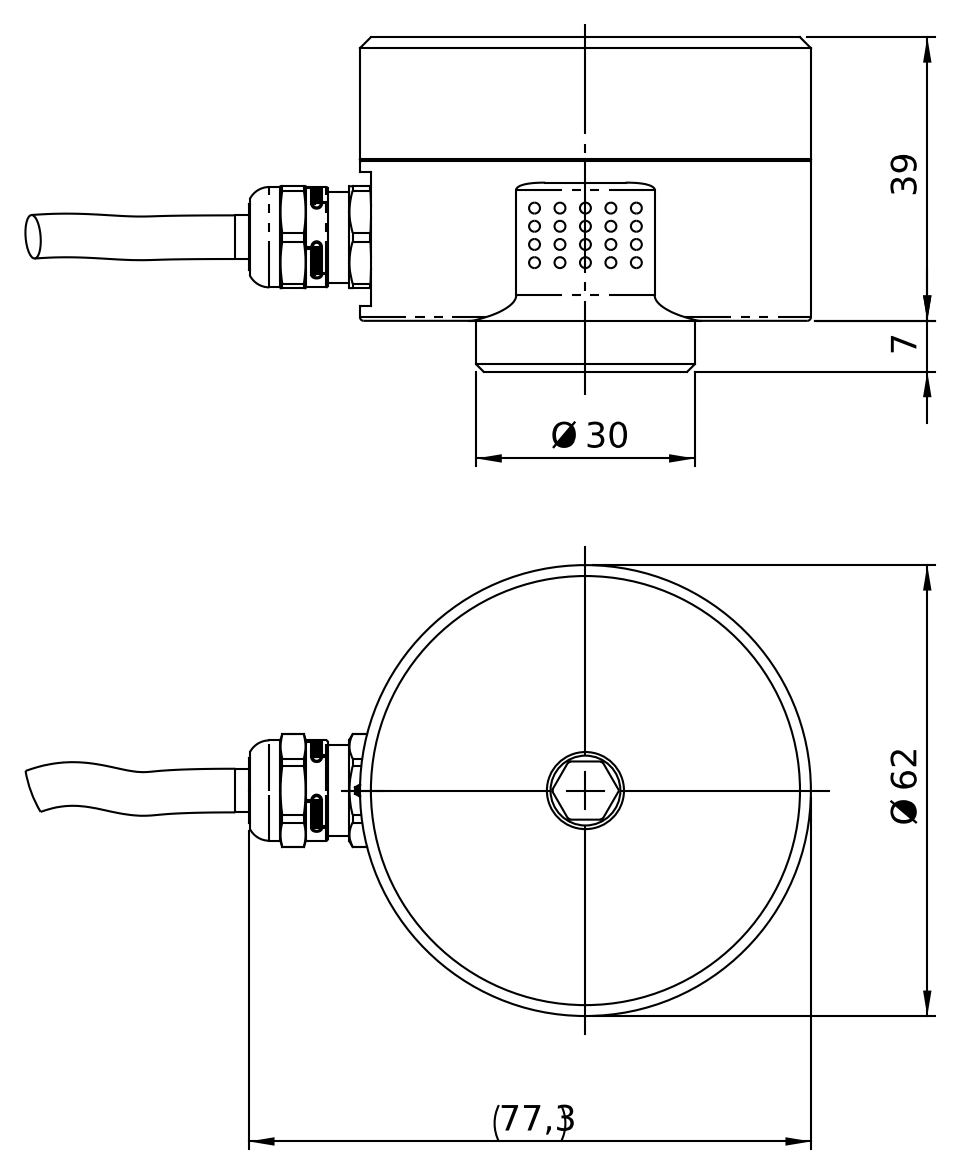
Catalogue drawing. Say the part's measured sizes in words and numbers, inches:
The part is named "02.117.022". Its 3-D file was written by "SolidWorks 2020 (AUTOMOTIVE_DESIGN)". It is 1 solid with 524 faces: 368 planar, 84 cylindrical and 72 other. Overall it measures 4.252 by 2.441 by 1.811 inches. Its volume is 7.271 cubic inches and its surface area 27.91 square inches. Round holes: 1 of diameter 0.256, 1 of diameter 0.354, 1 of diameter 0.378, 1 of diameter 0.444, 1 of diameter 0.587, 1 of diameter 0.591. Round bosses or shafts: 1 of diameter 2.441, 1 of diameter 1.181, 1 of diameter 0.543, 1 of diameter 0.492, 1 of diameter 0.354, 1 of diameter 0.236. Partial cylindrical surfaces (rounded edges, fillets, slot ends): 5 of radius 0.029, 4 of radius 0.006, 4 of radius 0.011, 4 of radius 0.021, 4 of radius 0.021, 2 of radius 0.039, 2 of radius 0.138, 1 of radius 0.264. The main face-to-face distances are 1.535, 0.276, 1.811, 2.323, 0.315, 0.039, 1.004, 0.551, 1.496, 0.669.
